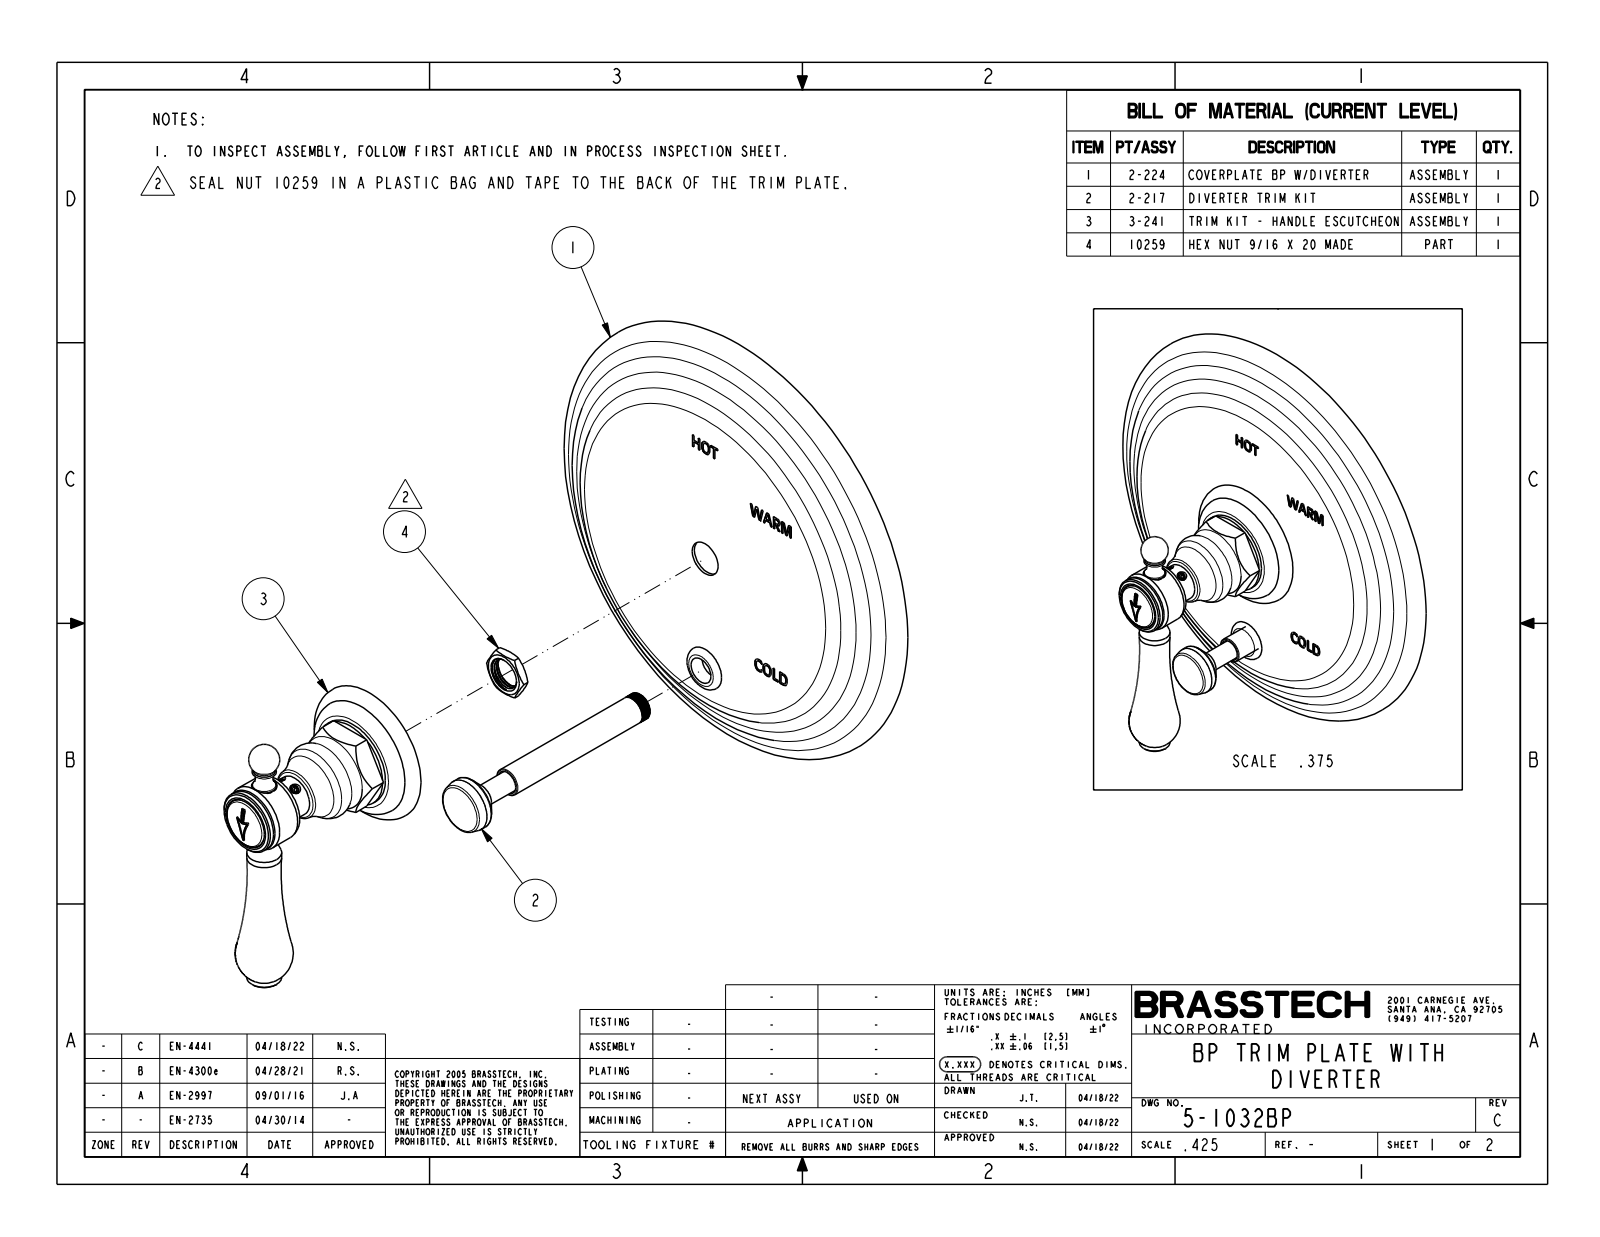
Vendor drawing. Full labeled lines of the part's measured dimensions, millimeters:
Part name (STEP PRODUCT): 5-1032BP
STEP written by: CREO PARAMETRIC BY PTC INC, 2018400 (CONFIG_CONTROL_DESIGN)
Units: millimetres
Bodies: 1 solid, 329 faces (146 planar, 37 cylindrical, 146 other)
Overall size (bounding box): 196.9 × 196.9 × 92.9
Volume: 538 200 mm³ · Surface area: 79 160 mm²
Round holes (diameter × count): ⌀10.4 ×1, ⌀21.7 ×1
Round bosses / shafts (diameter × count): ⌀37.6 ×1, ⌀28.3 ×1, ⌀26.8 ×1, ⌀22.9 ×1, ⌀17.4 ×1, ⌀14.3 ×1, ⌀12 ×1, ⌀10.2 ×1
Partial cylindrical surfaces — rounded edges, fillets, slot ends (radius × count): R0.4 ×2, R25.4 ×2, R25.9 ×2, R0.5 ×1
Main face-to-face distances: 19.2, 33.4, 58.1, 38.9, 62, 42.8, 3.9, 28.7, 9.5, 29.4
